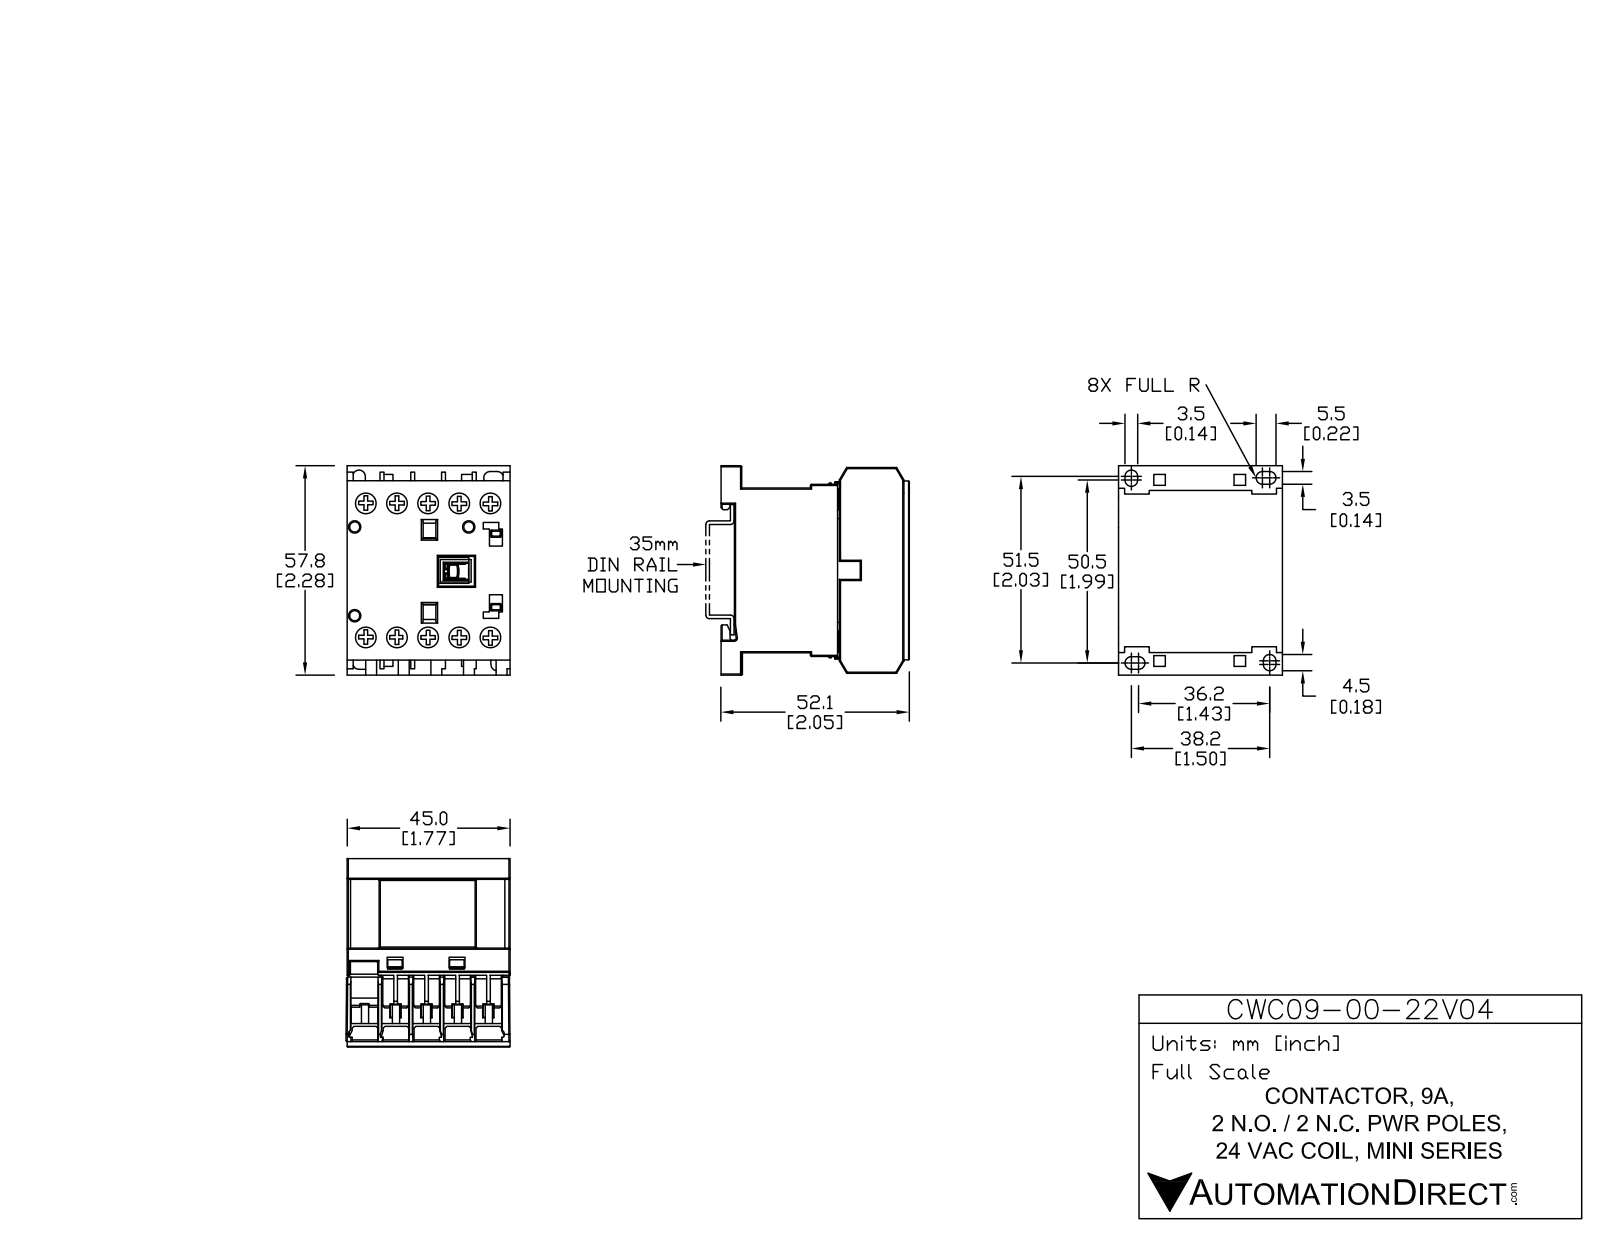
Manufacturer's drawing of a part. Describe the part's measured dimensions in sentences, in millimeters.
The part is named "CWC09-00-22V04". Its 3-D file was written by "SolidWorks 2013 (AUTOMOTIVE_DESIGN)". It is 15 solids with 535 faces: 445 planar, 90 cylindrical and 0 other. Overall it measures 58.04 by 52.12 by 45.75 millimeters. Its volume is 97 133 cubic millimeters and its surface area 30 437 square millimeters. Round holes: 10 of diameter 6.2, 3 of diameter 2.8. Round bosses or shafts: 10 of diameter 5.9. Partial cylindrical surfaces (rounded edges, fillets, slot ends): 20 of radius 0.3, 6 of radius 1.72, 2 of radius 1.73, 1 of radius 0.32, 1 of radius 0.42, 1 of radius 0.55. The main face-to-face distances are 8.25, 45.5, 1.25, 16.5, 9.5, 5.5, 17.75, 5.13, 10.63, 7. The hole center spacings are 8.55, 37.94, 17.1, 40.72, 36.96, 25.65, 44.99, 6.91.
